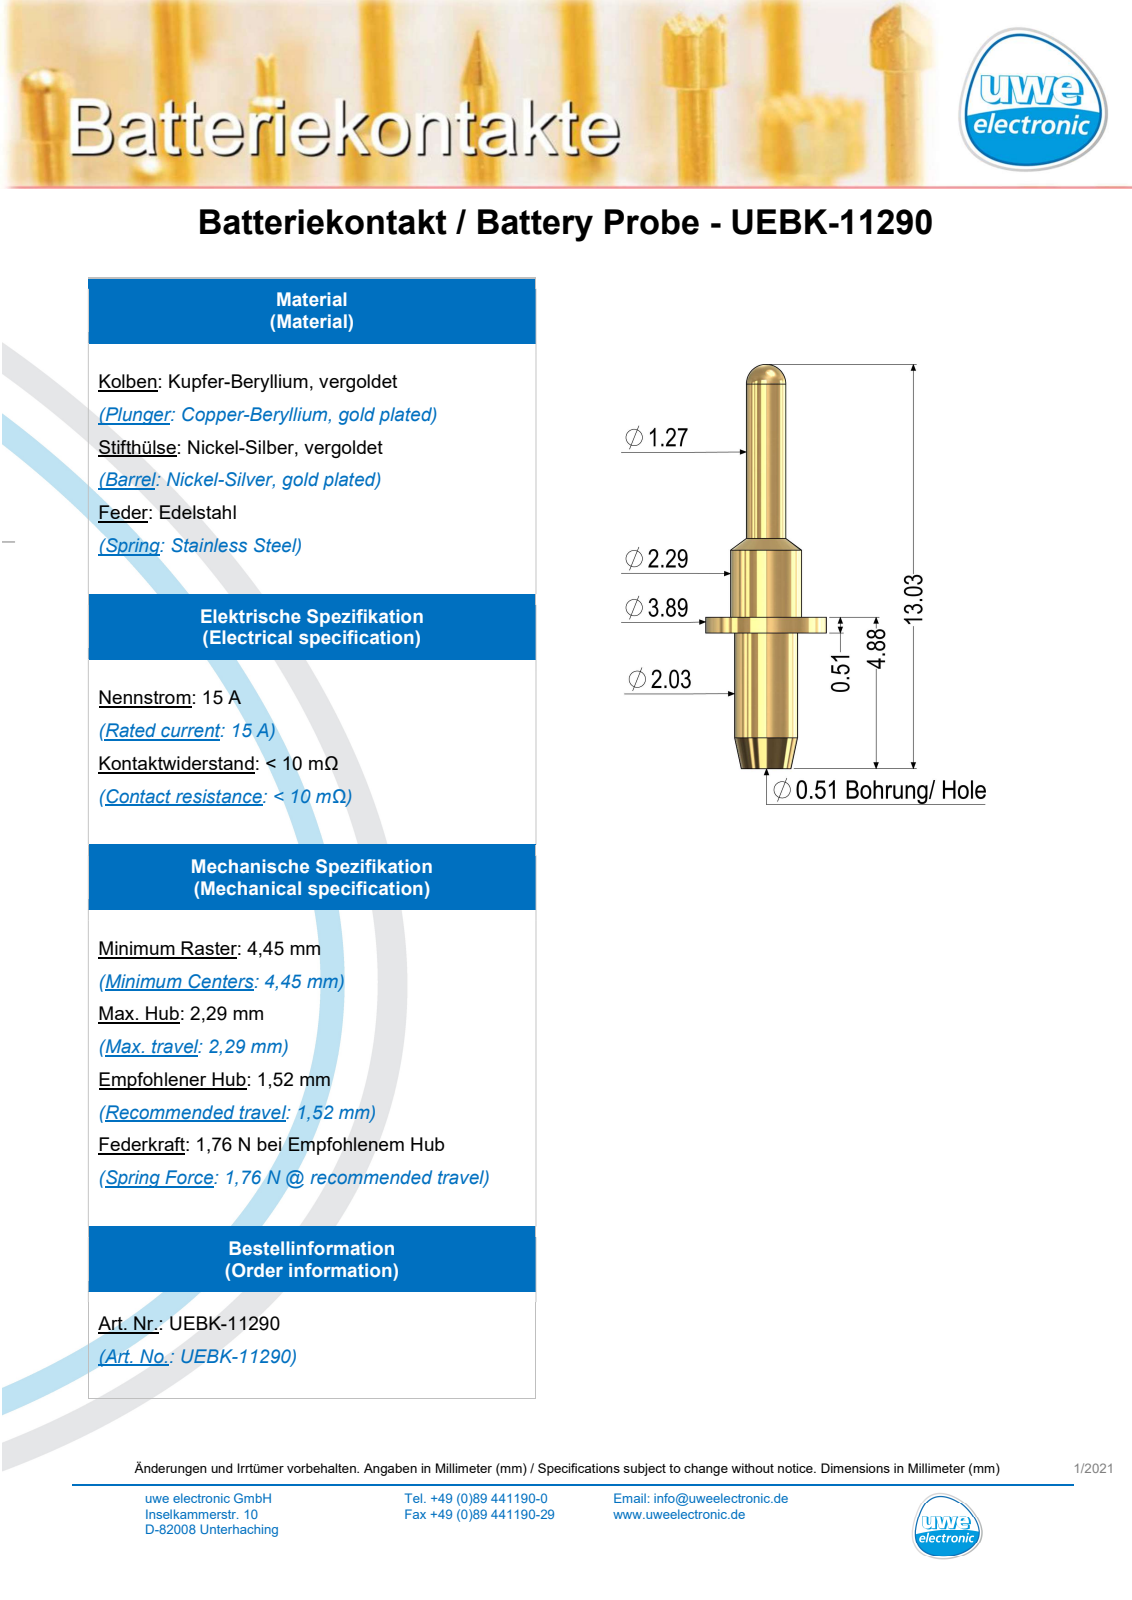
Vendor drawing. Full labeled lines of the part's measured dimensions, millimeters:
Part name (STEP PRODUCT): UEBK-11290
STEP written by: SolidWorks 2016 (AUTOMOTIVE_DESIGN)
Units: millimetres
Bodies: 1 solid, 20 faces (4 planar, 10 cylindrical, 6 other)
Overall size (bounding box): 13.03 × 3.89 × 3.89
Volume: 36 mm³ · Surface area: 94 mm²
Round holes (diameter × count): ⌀0.51 ×1
Round bosses / shafts (diameter × count): ⌀3.89 ×1, ⌀2.29 ×1, ⌀2.03 ×1, ⌀1.27 ×1
Main face-to-face distances: 0.51, 4.37, 4.88, 0.4, 3.97, 4.48
